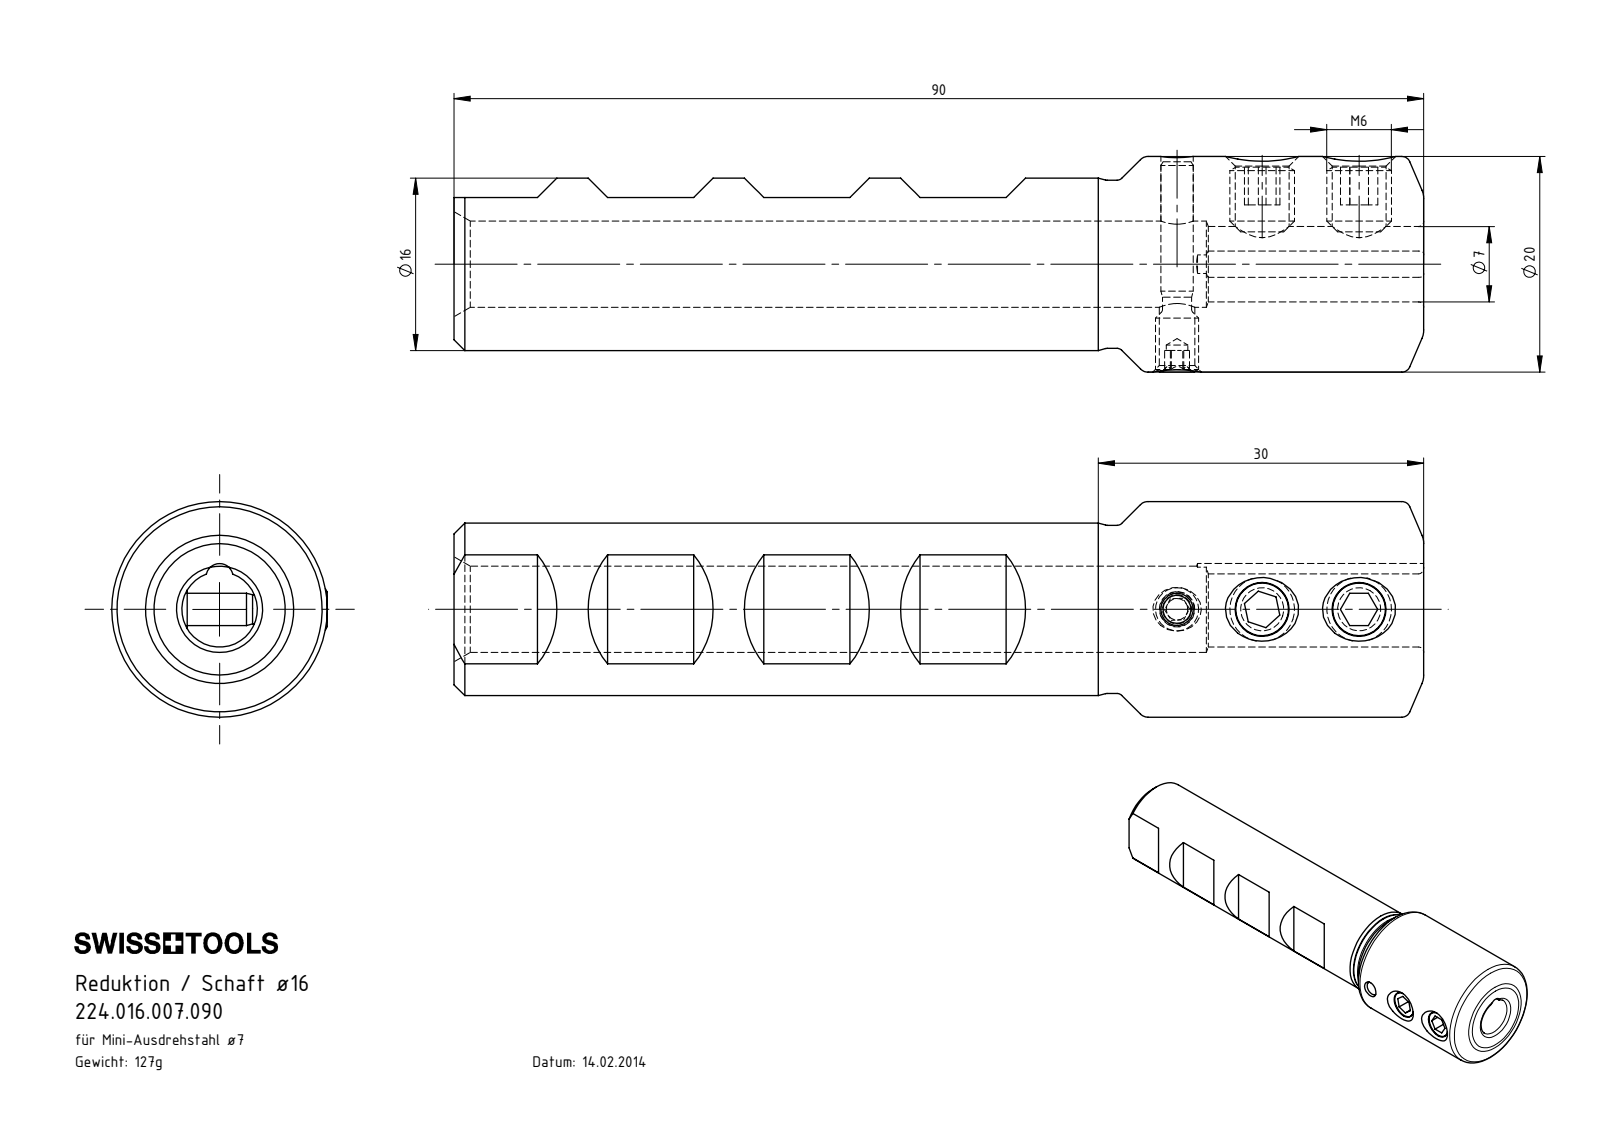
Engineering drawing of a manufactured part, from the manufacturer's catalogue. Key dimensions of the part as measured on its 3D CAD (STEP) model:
Part name (STEP PRODUCT): U0X-U16.0XX.090_A_Adapter 7; Axx-BG4.003.xxx_A_Adapter 7; ISO 4026 - M6 x 6; 224.016.007.090
STEP written by: SolidWorks 2017 (CONFIG_CONTROL_DESIGN)
Units: millimetres
Bodies: 4 solids, 130 faces (45 planar, 31 cylindrical, 54 other)
Overall size (bounding box): 90 × 20 × 20
Volume: 16 219 mm³ · Surface area: 8 239 mm²
Round holes (diameter × count): ⌀5 ×2, ⌀2 ×1, ⌀3 ×1, ⌀3.3 ×1, ⌀7 ×1, ⌀8 ×1
Round bosses / shafts (diameter × count): ⌀6 ×2, ⌀20 ×1, ⌀16 ×1, ⌀15.6 ×1, ⌀4 ×1, ⌀2.7 ×1
Partial cylindrical surfaces — rounded edges, fillets, slot ends (radius × count): R1.25 ×1
Main face-to-face distances: 10.25, 90, 20.5, 3, 6, 30.75, 2.5, 3.5, 3.22, 3.2
Hole centre spacings: 7.9, 9, 16.9
